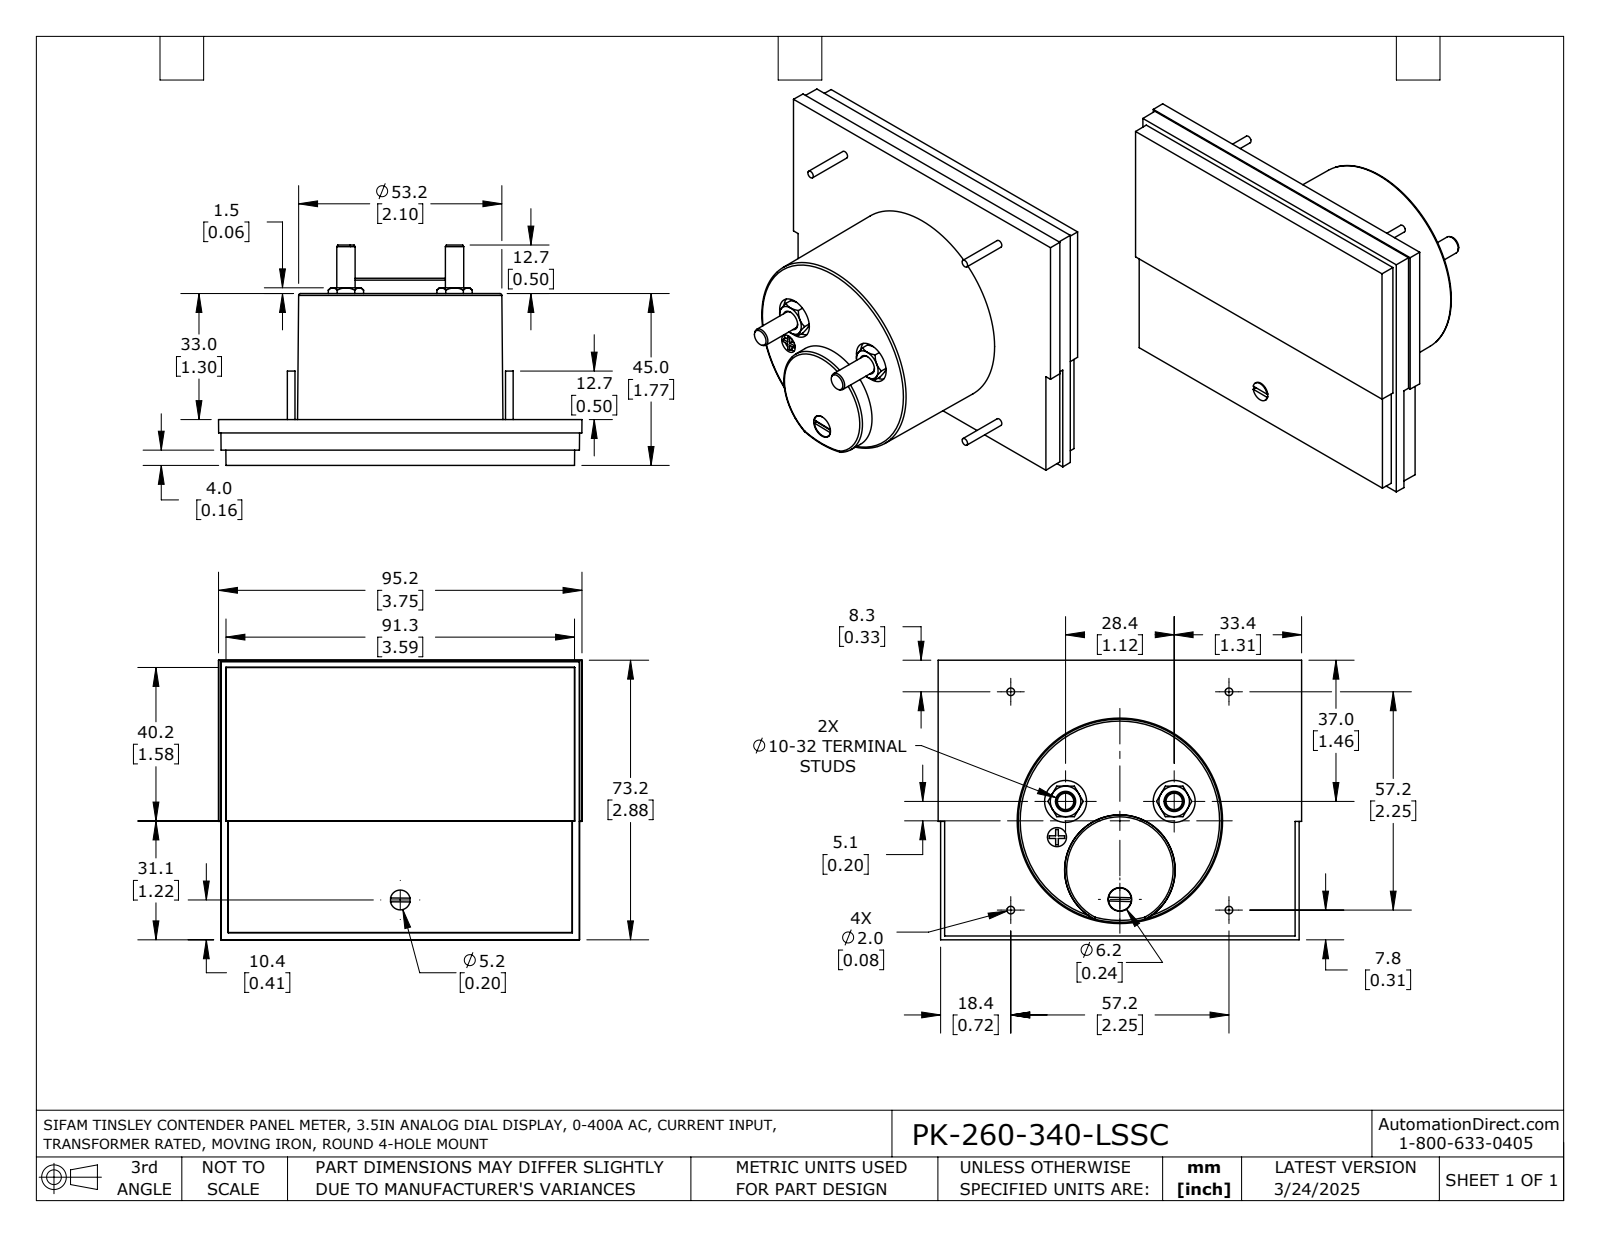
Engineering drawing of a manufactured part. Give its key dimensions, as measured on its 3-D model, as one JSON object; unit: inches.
{"part_name": "PK-260-340-LSSC", "step_written_by": "SolidWorks 2021 (AUTOMOTIVE_DESIGN)", "units": "inches", "bodies": {"solids": 1, "faces": 163, "planar": 76, "cylindrical": 31, "other": 56}, "overall_size": [3.748, 2.882, 2.272], "volume_in3": 9.446, "surface_area_in2": 38.39, "round_holes": [[0.433, 2], [0.197, 1], [0.244, 1]], "round_bosses_or_shafts": [[0.079, 4], [0.189, 2], [0.236, 1], [0.205, 1]], "partial_cylinders_radius": [[0.1, 1]], "face_to_face_distances": [0.472, 0.03, 0.443, 1.772, 1.299, 1.742, 0.157, 0.073, 0.315, 1.457], "hole_center_spacings": [1.155, 0.379, 0.912, 1.12, 1.263]}
